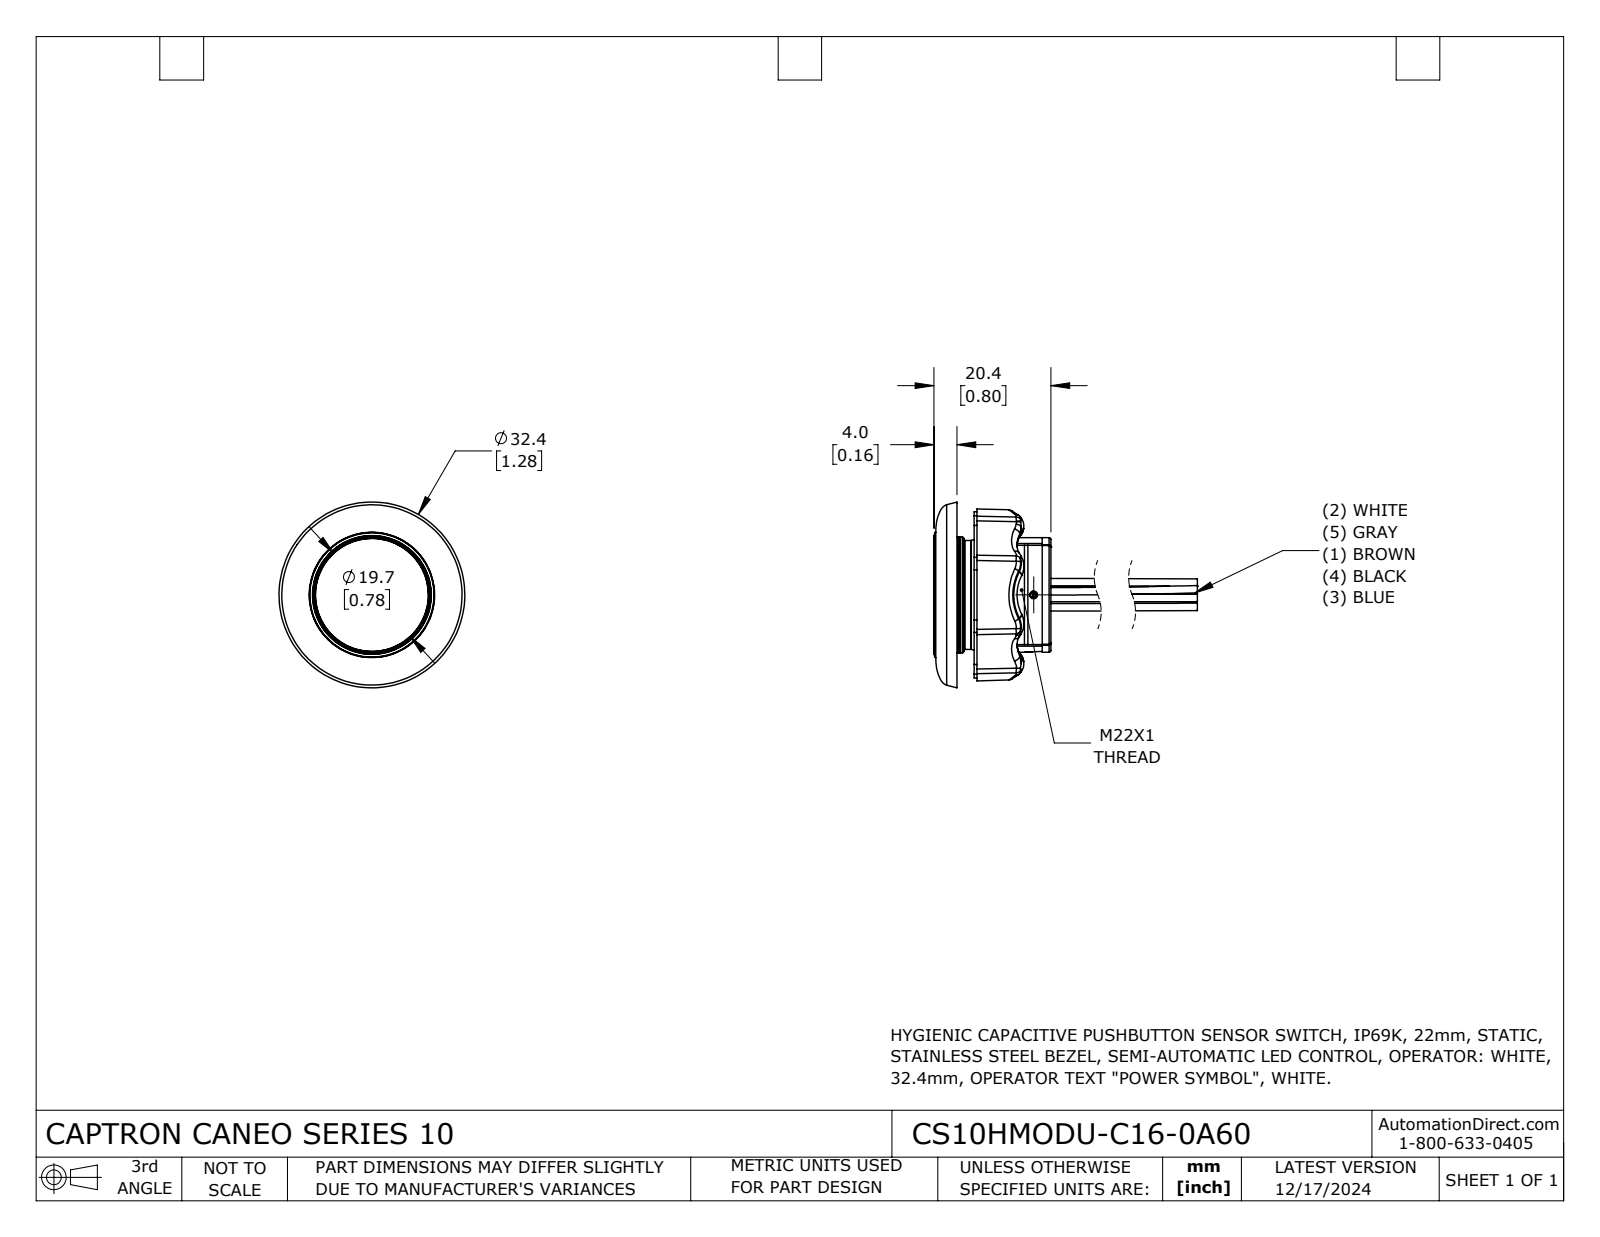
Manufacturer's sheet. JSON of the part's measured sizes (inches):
{"part_name": "CS10HMODU-C16-0A60", "step_written_by": "SolidWorks 2024 (CONFIG_CONTROL_DESIGN)", "units": "inches", "bodies": {"solids": 7, "faces": 854, "planar": 403, "cylindrical": 138, "other": 313}, "overall_size": [1.803, 1.277, 1.277], "volume_in3": 0.636, "surface_area_in2": 9.99, "round_holes": [[0.053, 1], [0.827, 1], [0.927, 1], [1.004, 1]], "round_bosses_or_shafts": [[0.748, 1], [0.724, 1]], "partial_cylinders_radius": [[0.006, 20], [0.004, 6], [0.118, 6], [0.295, 6], [0.012, 4], [0.039, 4], [0.689, 4], [0.196, 1]], "face_to_face_distances": [0.157, 0.646, 0.803, 0.134, 0.016, 0.528, 0.142, 0.118, 0.276, 0.661]}
